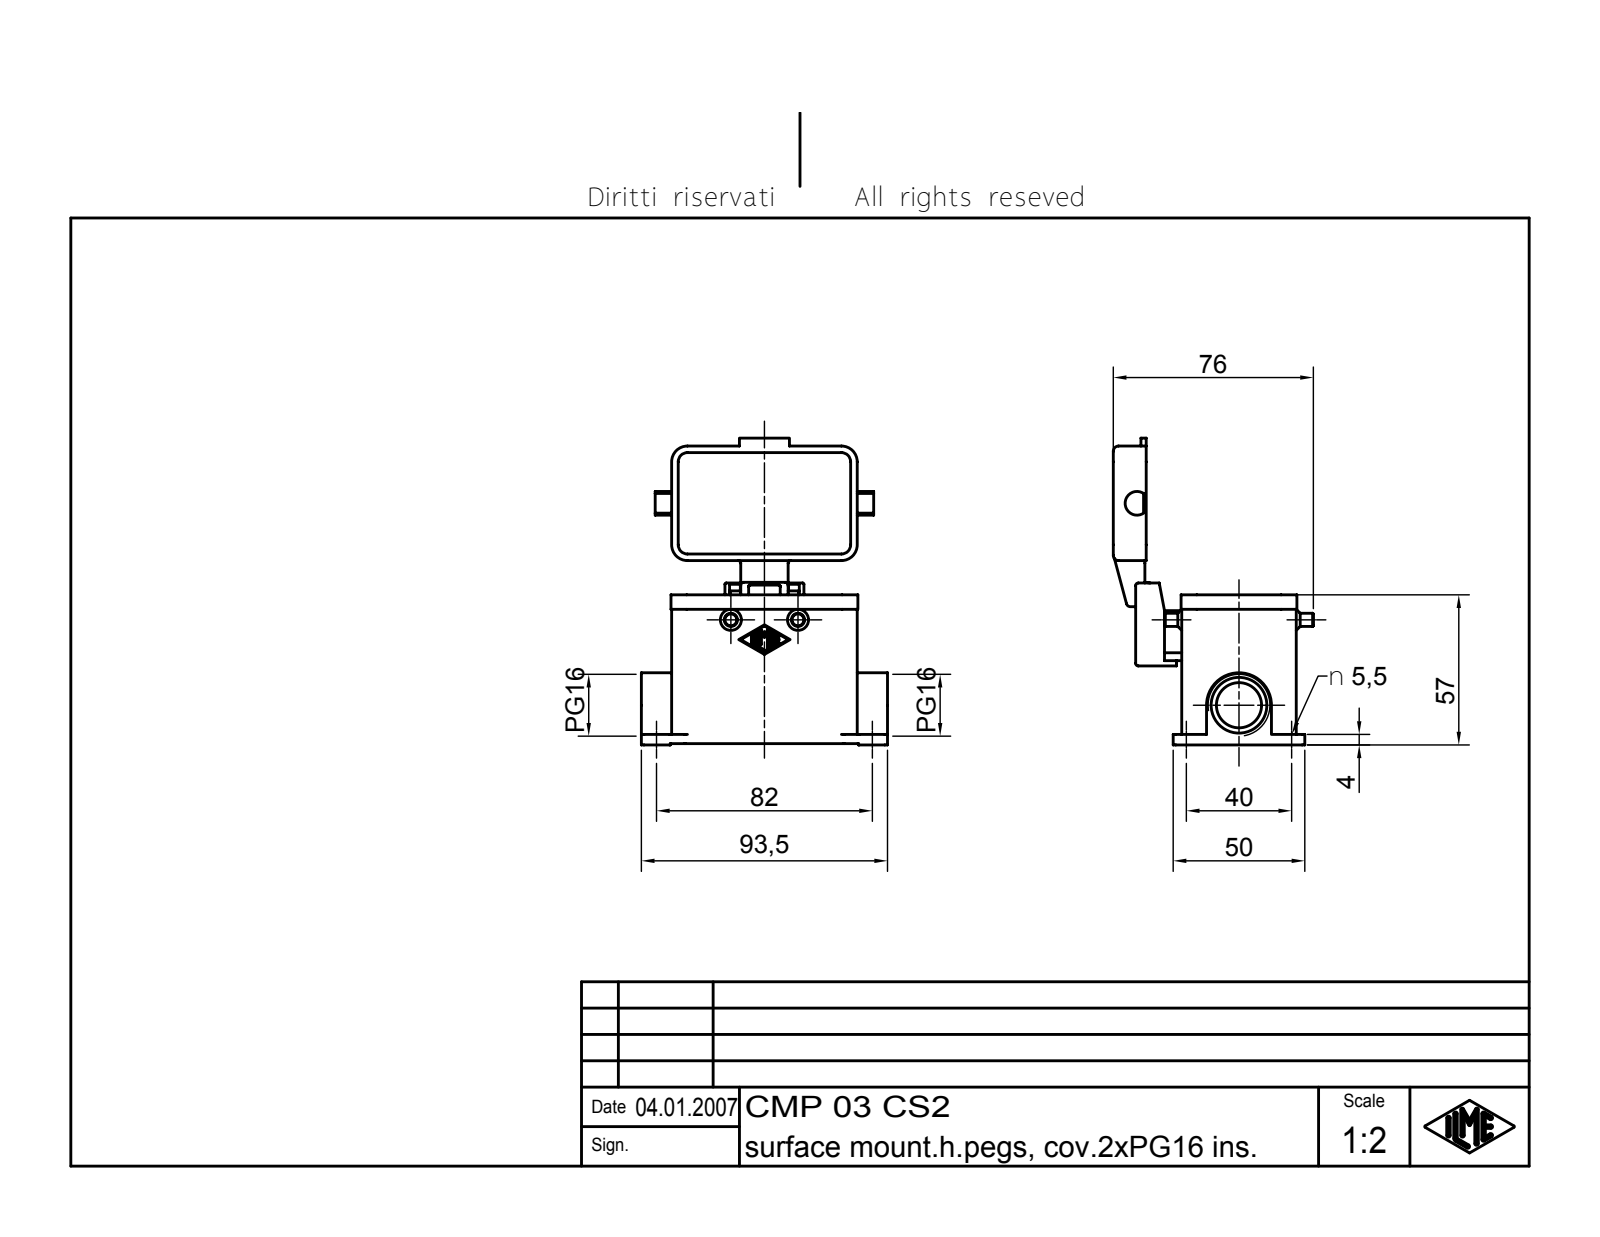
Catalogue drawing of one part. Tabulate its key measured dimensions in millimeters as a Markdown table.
| quantity | value |
| --- | --- |
| part name | CMP 03 CS2 |
| STEP written by | Autodesk Inventor 7 (AUTOMOTIVE_DESIGN) |
| units | millimeters |
| bodies | 2 solids, 470 faces (177 planar, 177 cylindrical, 116 other) |
| overall size | 116.5 × 93.5 × 76 |
| volume | 93 085 mm³ |
| surface area | 51 674 mm² |
| round holes (diameter × count) | 5.5 × 4, 4 × 1, 5 × 1, 17.16 × 1, 21.16 × 1 |
| round bosses / shafts (diameter × count) | 5 × 2, 3 × 2, 7 × 1, 4 × 1 |
| partial cylindrical surfaces (radius × count) | 1 × 26, 0.38 × 14, 6 × 12, 0.5 × 9, 0.7 × 8, 2 × 8, 3 × 4, 3.5 × 4 |
| main face-to-face distances | 3, 40.5, 3.5, 43.5, 66, 69.5, 22.5, 26, 63, 66.5 |
| hole center spacings | 40, 82, 91.24 |
